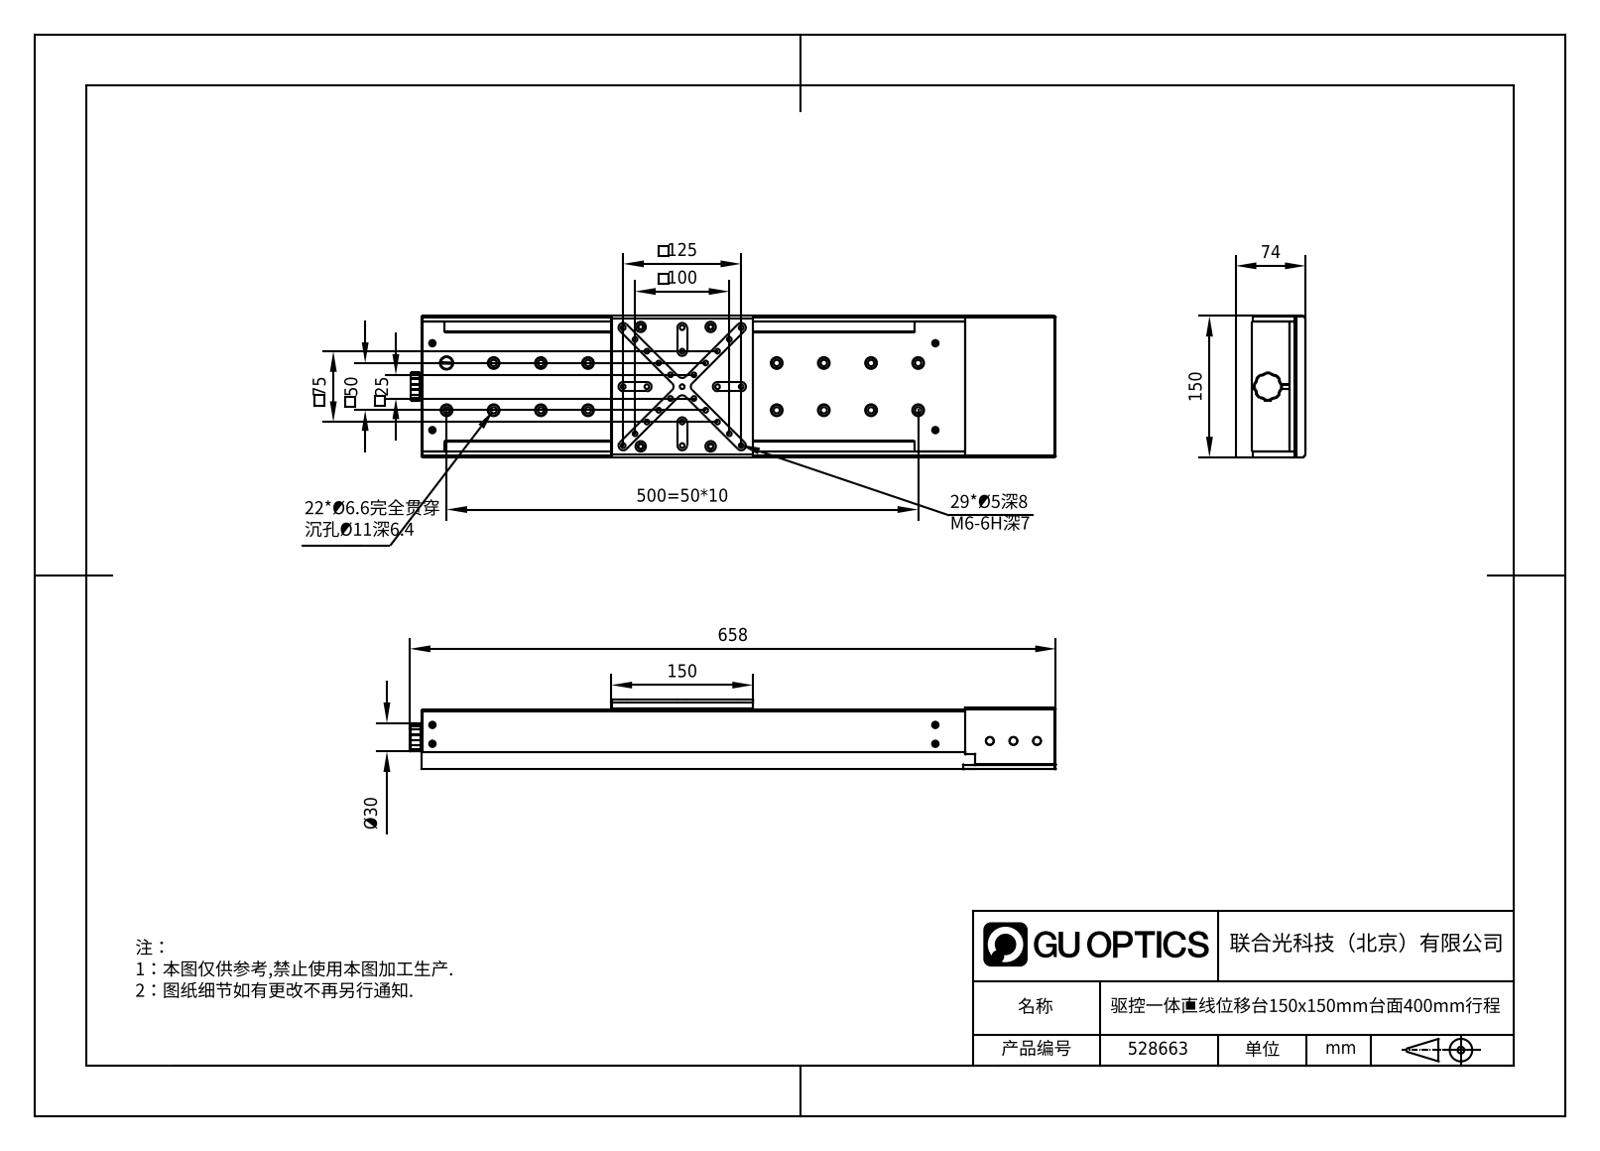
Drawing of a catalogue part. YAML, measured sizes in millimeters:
part_name: "528663"
step_written_by: "SolidWorks 2020 (CONFIG_CONTROL_DESIGN)"
units: millimeters
bodies: {solids: 45, faces: 2691, planar: 1418, cylindrical: 824, other: 449}
overall_size: [685, 150, 74]
volume: 3835000
surface_area: 853286
round_holes:
  - {diameter: 5, count: 40}
  - {diameter: 6.6, count: 28}
  - {diameter: 11, count: 28}
  - {diameter: 3.4, count: 27}
  - {diameter: 12.5, count: 22}
  - {diameter: 6.5, count: 19}
  - {diameter: 2.46, count: 16}
  - {diameter: 3.5, count: 16}
  - {diameter: 2.5, count: 15}
  - {diameter: 6, count: 12}
  - {diameter: 3.3, count: 9}
  - {diameter: 4.5, count: 6}
round_bosses_or_shafts:
  - {diameter: 38.2, count: 1}
  - {diameter: 24, count: 1}
  - {diameter: 19, count: 1}
  - {diameter: 16, count: 1}
  - {diameter: 14, count: 1}
  - {diameter: 10.56, count: 1}
  - {diameter: 3, count: 1}
partial_cylinders:
  - {radius: 1, count: 20}
  - {radius: 5, count: 16}
  - {radius: 2, count: 13}
  - {radius: 7.5, count: 8}
  - {radius: 4, count: 5}
  - {radius: 1.5, count: 4}
  - {radius: 0.3, count: 2}
  - {radius: 0.75, count: 2}
face_to_face_distances: [6, 39, 57, 18, 63, 45, 1, 144, 150, 17]
hole_center_spacings: [20, 25, 101.6, 32.02, 72.1, 76.31, 103.55, 124.58]
